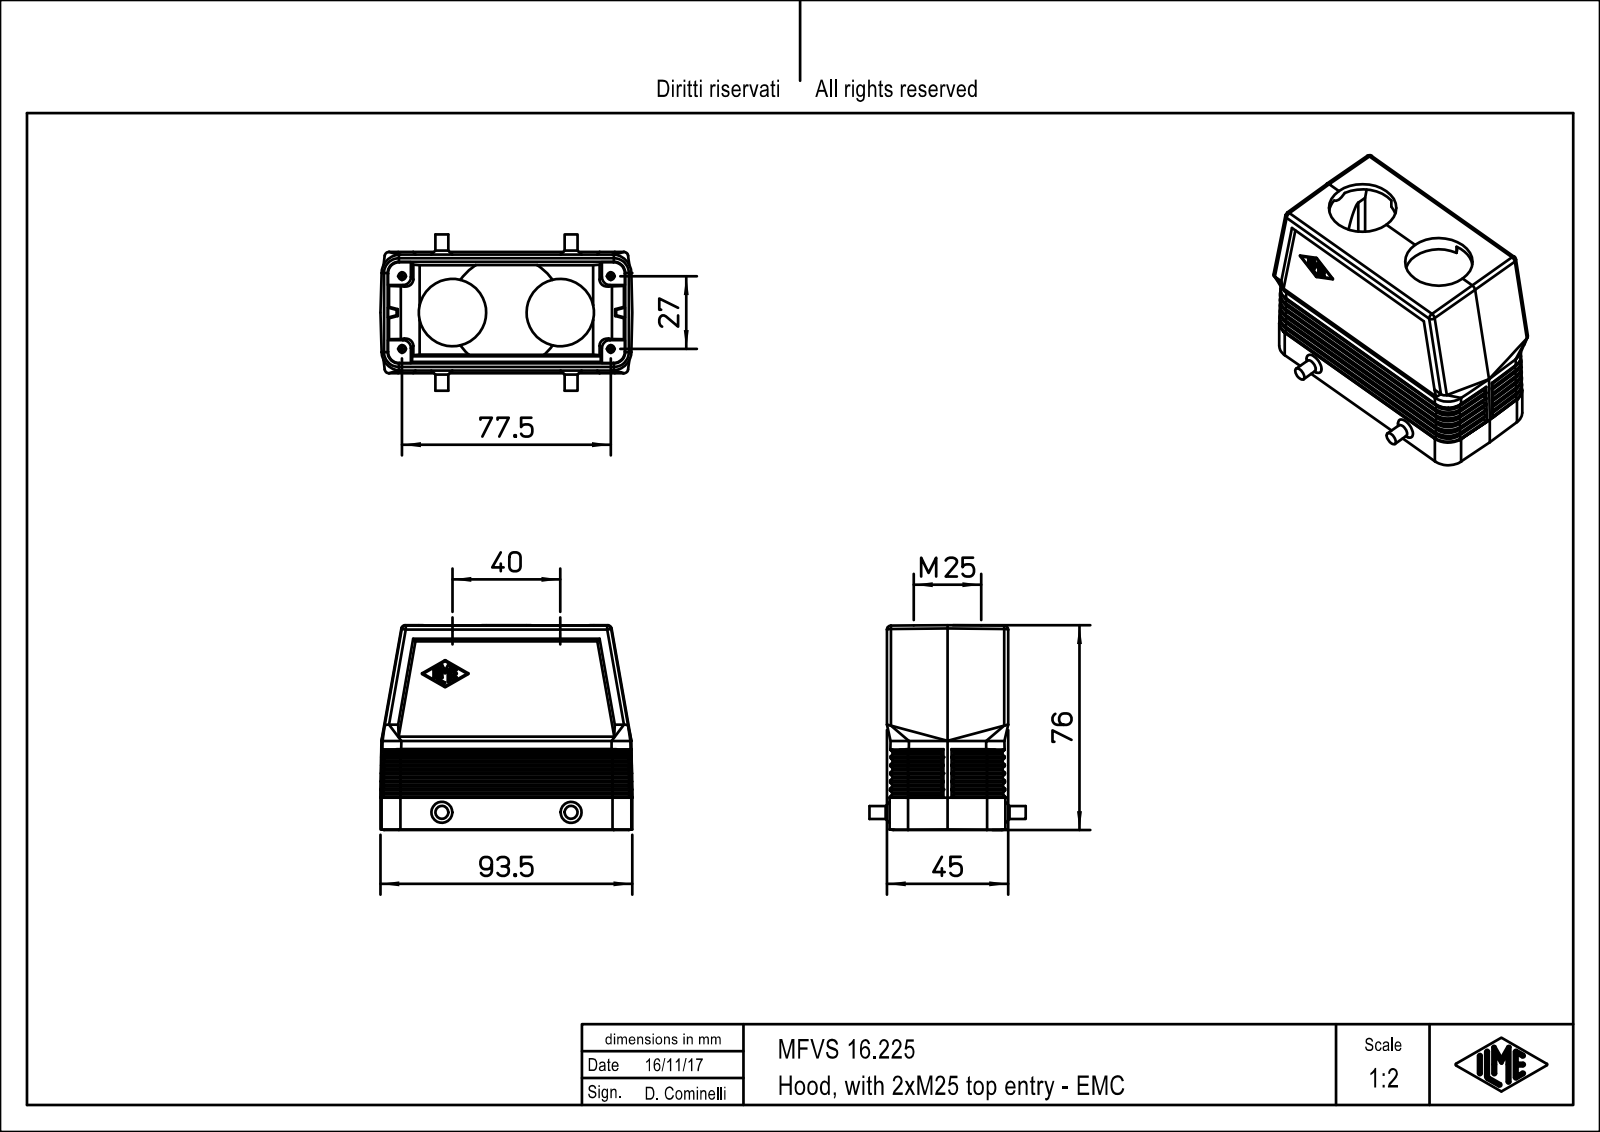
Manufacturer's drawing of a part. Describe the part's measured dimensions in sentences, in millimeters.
The part is named "MFVS_16.225". Its 3-D file was written by "PTC Creo Elements/Direct Modeling 19.0E 27-Jun-2016 (C) Parametric Technology GmbH (AUTOMOTIVE_DESIGN)". It is 1 solid with 481 faces: 209 planar, 128 cylindrical and 144 other. Overall it measures 93.5 by 76 by 58 millimeters. Its volume is 89 671 cubic millimeters and its surface area 43 102 square millimeters. Round holes: 2 of diameter 25. Round bosses or shafts: 2 of diameter 4.8. Partial cylindrical surfaces (rounded edges, fillets, slot ends): 78 of radius 0.5, 10 of radius 1.5, 8 of radius 7, 4 of radius 3, 4 of radius 4.2, 1 of radius 21. The main face-to-face distances are 43, 2.01, 2, 8.5, 4, 1, 44, 6, 6.01, 4.01. The hole center spacings are 40.
